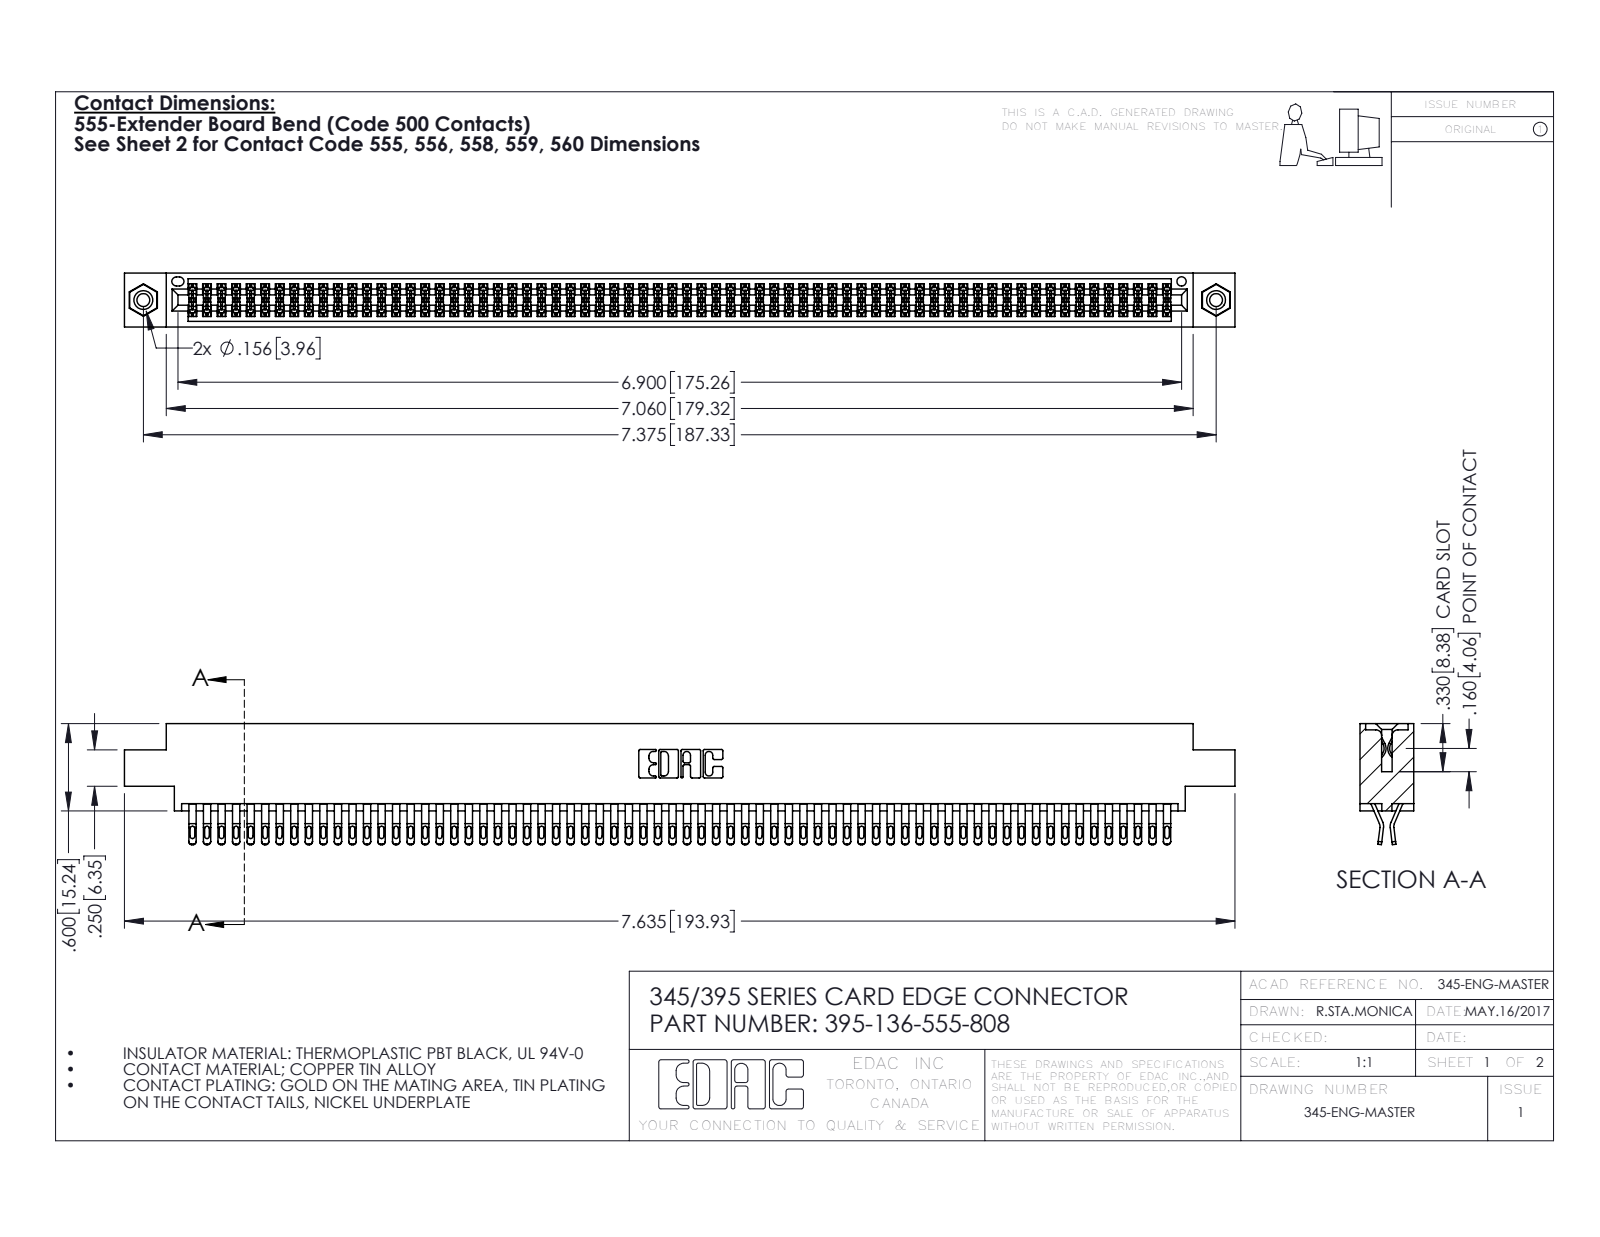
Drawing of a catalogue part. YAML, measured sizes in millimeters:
part_name: "345-292-001_555 Tail; 345 Part_0.170 Offset - 0.156 Dia-TI; 345-250-001_345-250-003-102; 395-136-555-808"
step_written_by: "SolidWorks 2016 (CONFIG_CONTROL_DESIGN)"
units: millimeters
bodies: {solids: 139, faces: 7806, planar: 4332, cylindrical: 3458, other: 16}
overall_size: [193.9, 21.1, 9.4]
volume: 19350
surface_area: 30640
round_holes:
  - {diameter: 2.3, count: 2}
  - {diameter: 3.2, count: 2}
  - {diameter: 4, count: 2}
  - {diameter: 1.6, count: 1}
round_bosses_or_shafts:
  - {diameter: 3.9, count: 2}
partial_cylinders:
  - {radius: 0.4, count: 340}
  - {radius: 0.5, count: 272}
  - {radius: 0.2, count: 204}
  - {radius: 0.3, count: 22}
  - {radius: 0.2, count: 6}
  - {radius: 0.8, count: 6}
  - {radius: 0.7, count: 3}
  - {radius: 0.3, count: 2}
face_to_face_distances: [1.8, 7.6, 0.6, 9.4, 5.1, 2.5, 6.9, 5.7, 4.4, 3.8]
hole_center_spacings: [6.9, 181.3, 187.3]
